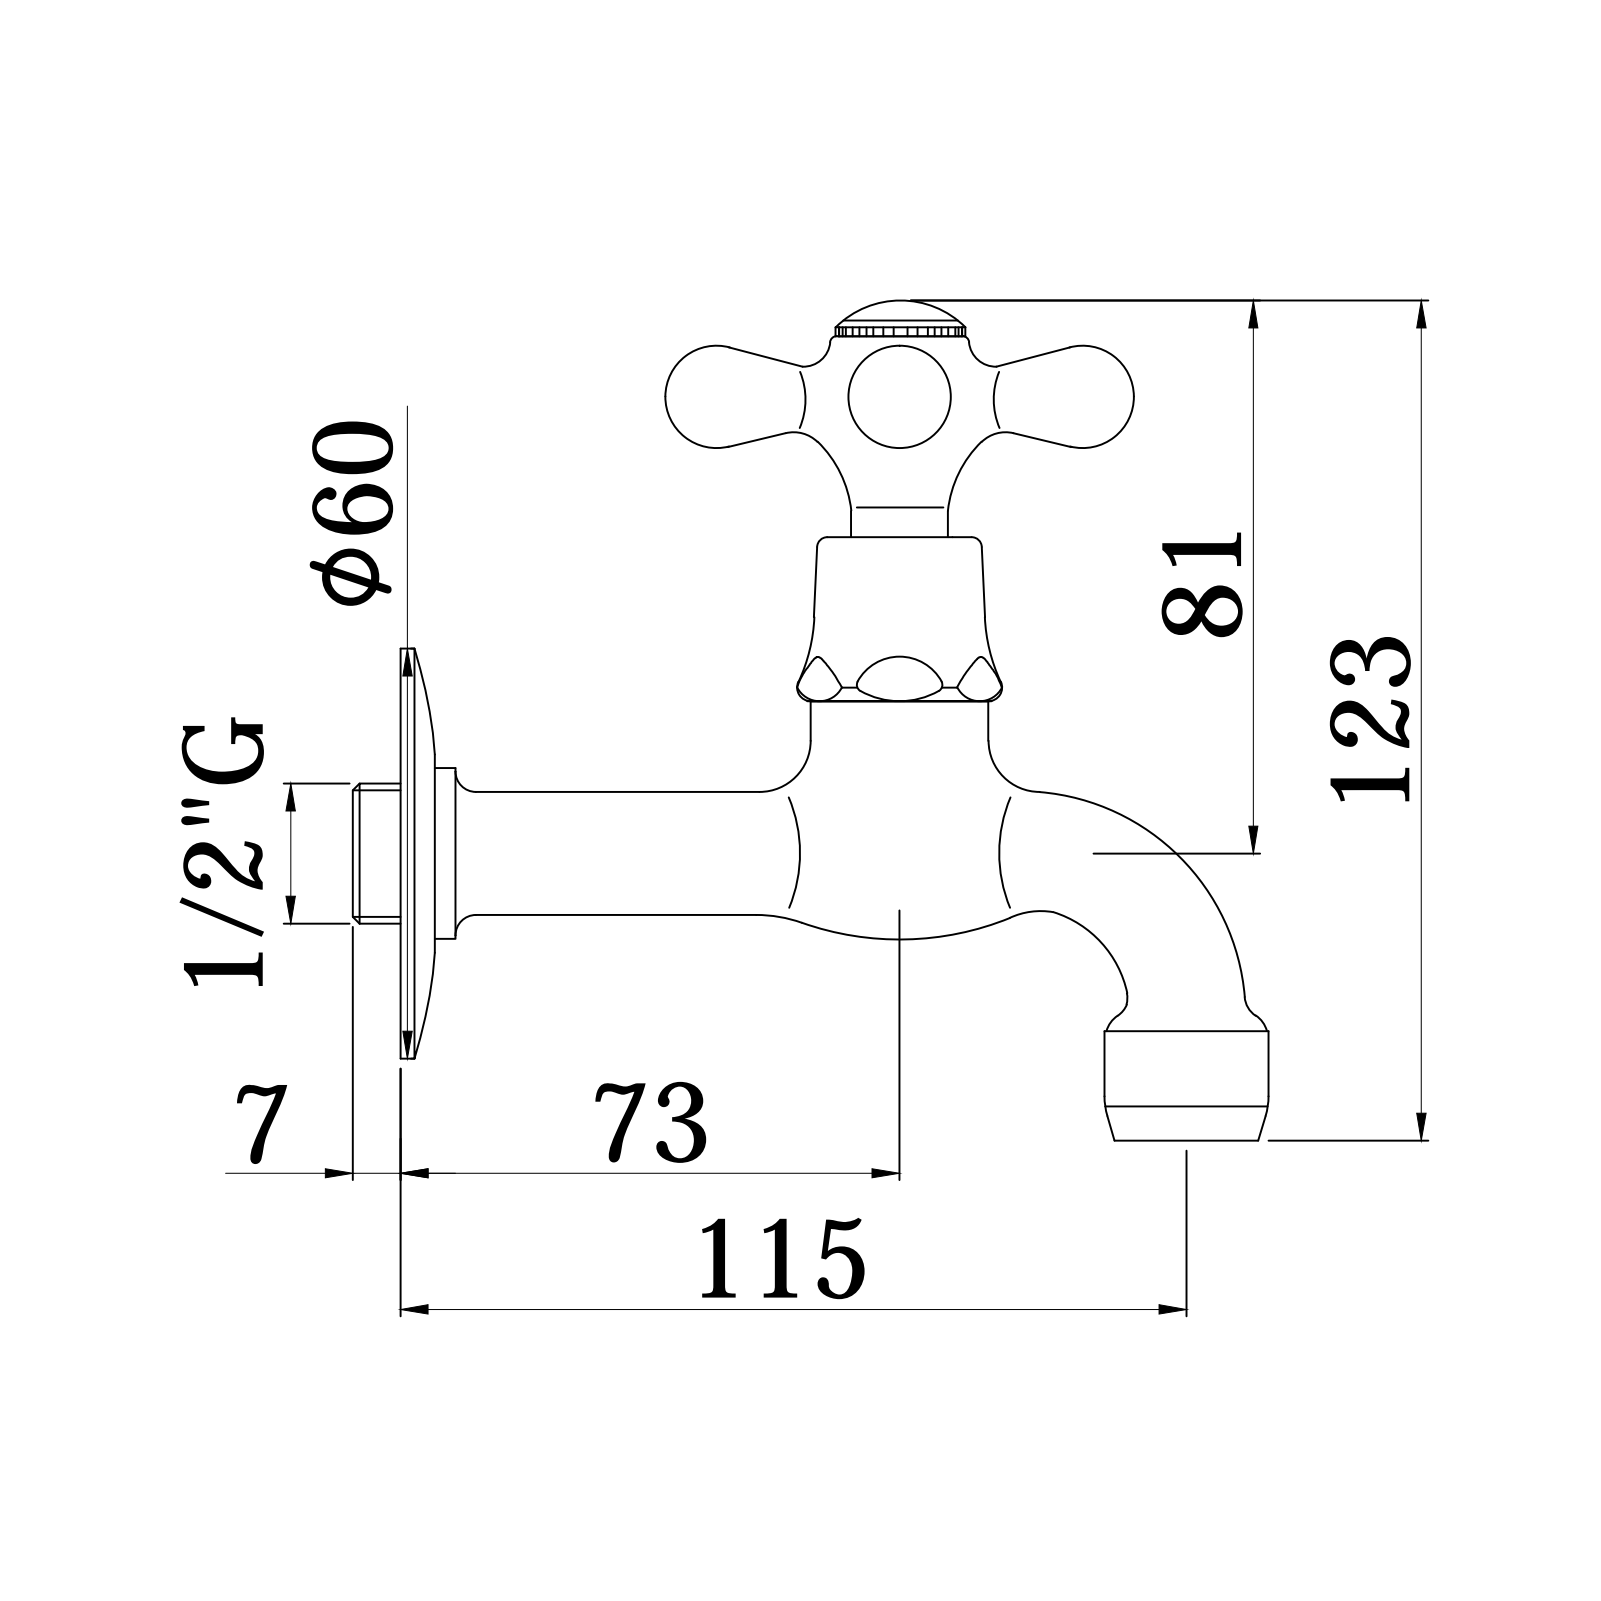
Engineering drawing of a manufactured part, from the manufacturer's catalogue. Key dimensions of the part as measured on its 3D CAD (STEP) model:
Part name (STEP PRODUCT): IRV213CR
STEP written by: CREO PARAMETRIC BY PTC INC, 2020044 (CONFIG_CONTROL_DESIGN)
Units: millimetres
Bodies: 1 solid, 147 faces (20 planar, 24 cylindrical, 103 other)
Overall size (bounding box): 126.8 × 125.25 × 72
Volume: 113 248 mm³ · Surface area: 24 954 mm²
Round bosses / shafts (diameter × count): ⌀58 ×1, ⌀26.5 ×1, ⌀24.7 ×1, ⌀23.6 ×1, ⌀22 ×1, ⌀21 ×1, ⌀18.8 ×1, ⌀18 ×1
Partial cylindrical surfaces — rounded edges, fillets, slot ends (radius × count): R14.5 ×1
Main face-to-face distances: 26.5, 7.7, 90.55, 90.35, 53.25, 79.75, 45.55, 72.05, 13, 5.3
